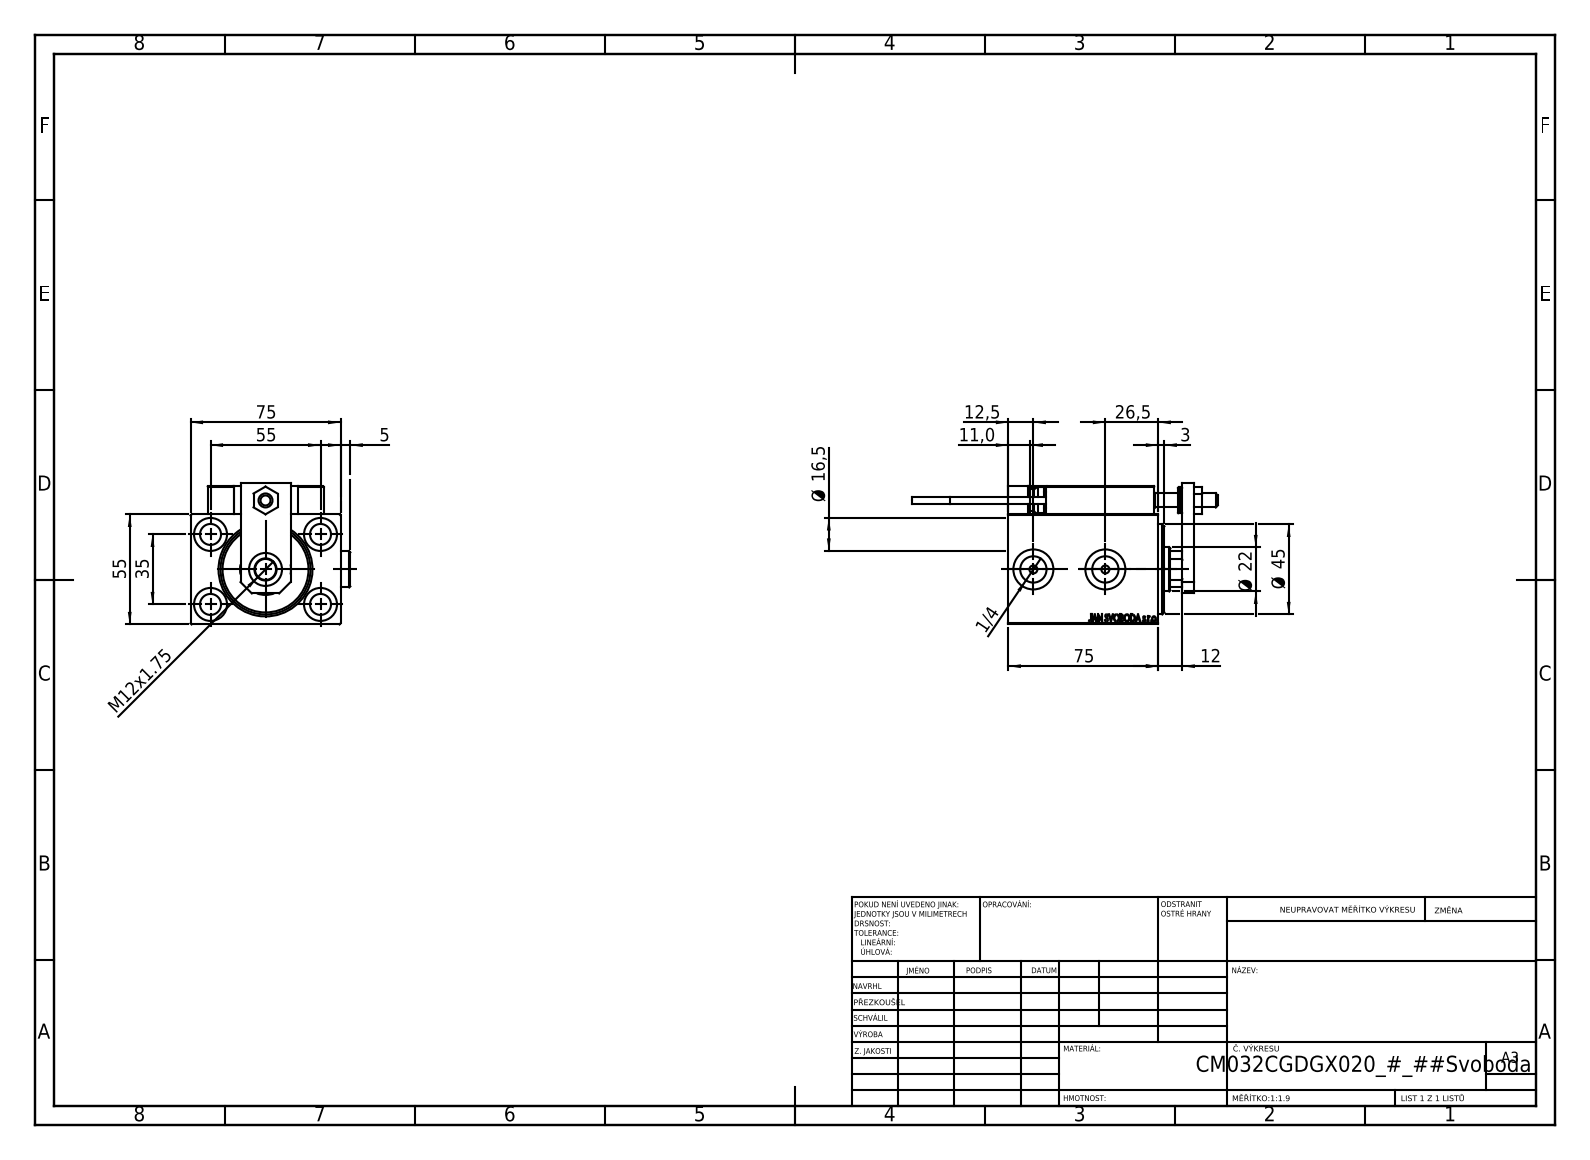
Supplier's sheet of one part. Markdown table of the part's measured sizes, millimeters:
| quantity | value |
| --- | --- |
| part name | V450CM_VC_B; SWITCH X; SWITCH_X_FRONT_BACK; V450CM_C_Body (+8 more) |
| STEP written by | SolidWorks 2019 (CONFIG_CONTROL_DESIGN) |
| units | millimeters |
| bodies | 25 solids, 1336 faces (594 planar, 204 cylindrical, 538 other) |
| overall size | 152.7 × 79.9 × 70.5 |
| volume | 311 696 mm³ |
| surface area | 87 420 mm² |
| round holes (diameter × count) | 4 × 6, 8 × 5, 10.5 × 5, 16.5 × 5, 3.2 × 4, 5 × 2, 13.16 × 2, 20 × 2, 7 × 1, 22 × 1, 25.5 × 1, 32 × 1 |
| round bosses / shafts (diameter × count) | 18 × 2, 5 × 2, 3.8 × 2, 13 × 1, 11 × 1 |
| partial cylindrical surfaces (radius × count) | 0.3 × 30, 3 × 2, 10.5 × 1 |
| main face-to-face distances | 55, 75, 14, 10, 12, 7, 5, 69, 25, 20 |
| hole center spacings | 32.6, 11.37, 20, 27.07, 29.59, 29.69, 32.33, 34.83 |
